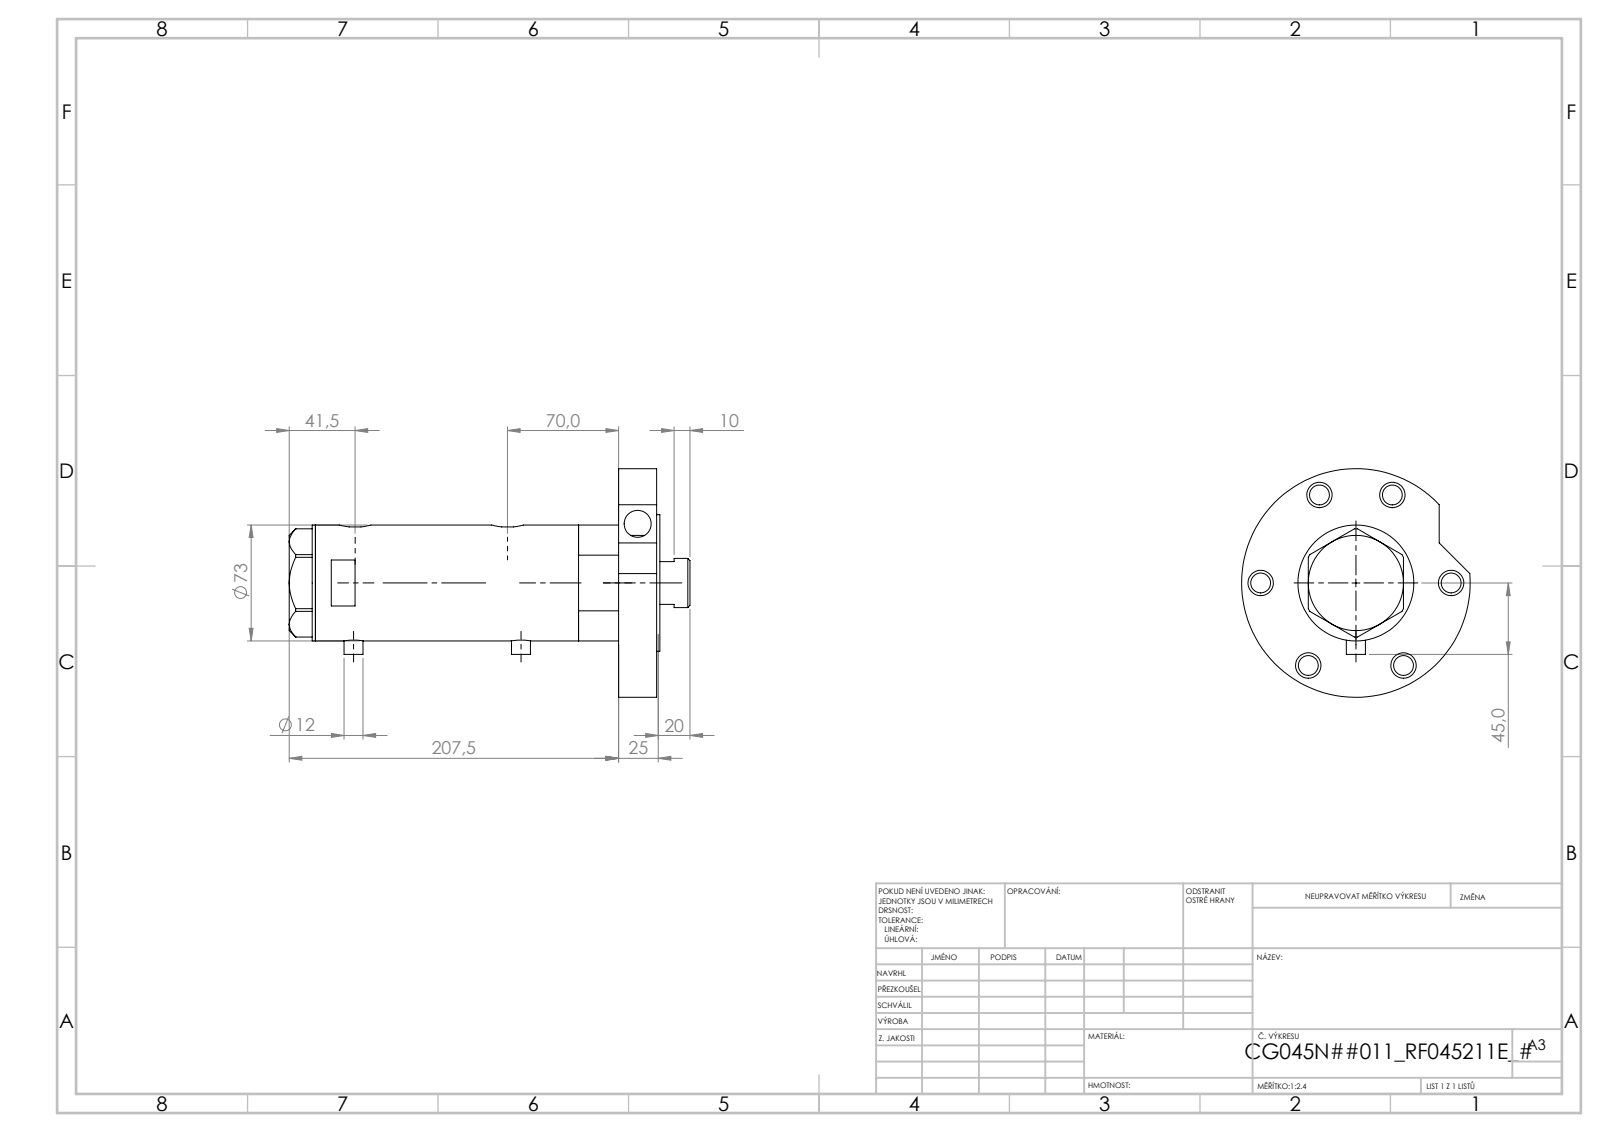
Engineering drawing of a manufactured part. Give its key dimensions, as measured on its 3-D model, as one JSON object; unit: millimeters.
{"part_name": "V270CG_RF211E; V270CG_BACK; V270CG_FRONT; V270CG_VC (+1 more)", "step_written_by": "SolidWorks 2019 (CONFIG_CONTROL_DESIGN)", "units": "millimeters", "bodies": {"solids": 5, "faces": 169, "planar": 61, "cylindrical": 88, "other": 20}, "overall_size": [202.52, 144, 144], "volume_mm3": 977983, "surface_area_mm2": 177635, "round_holes": [[12.5, 8], [16, 6], [5, 2], [13.16, 2], [10.5, 1], [17, 1], [32, 1], [33.5, 1], [45, 1], [48, 1], [60, 1], [64, 1]], "round_bosses_or_shafts": [[12, 2], [144, 1], [86, 1], [73, 1], [58, 1], [31, 1]], "partial_cylinders_radius": [[10, 2]], "face_to_face_distances": [24, 138.46, 26, 162.46, 2, 164.46, 78.16, 60.3, 84.3, 52.16], "hole_center_spacings": [60, 62.65, 66.67, 99.77, 103.92, 107.62, 119.74, 0.99]}
